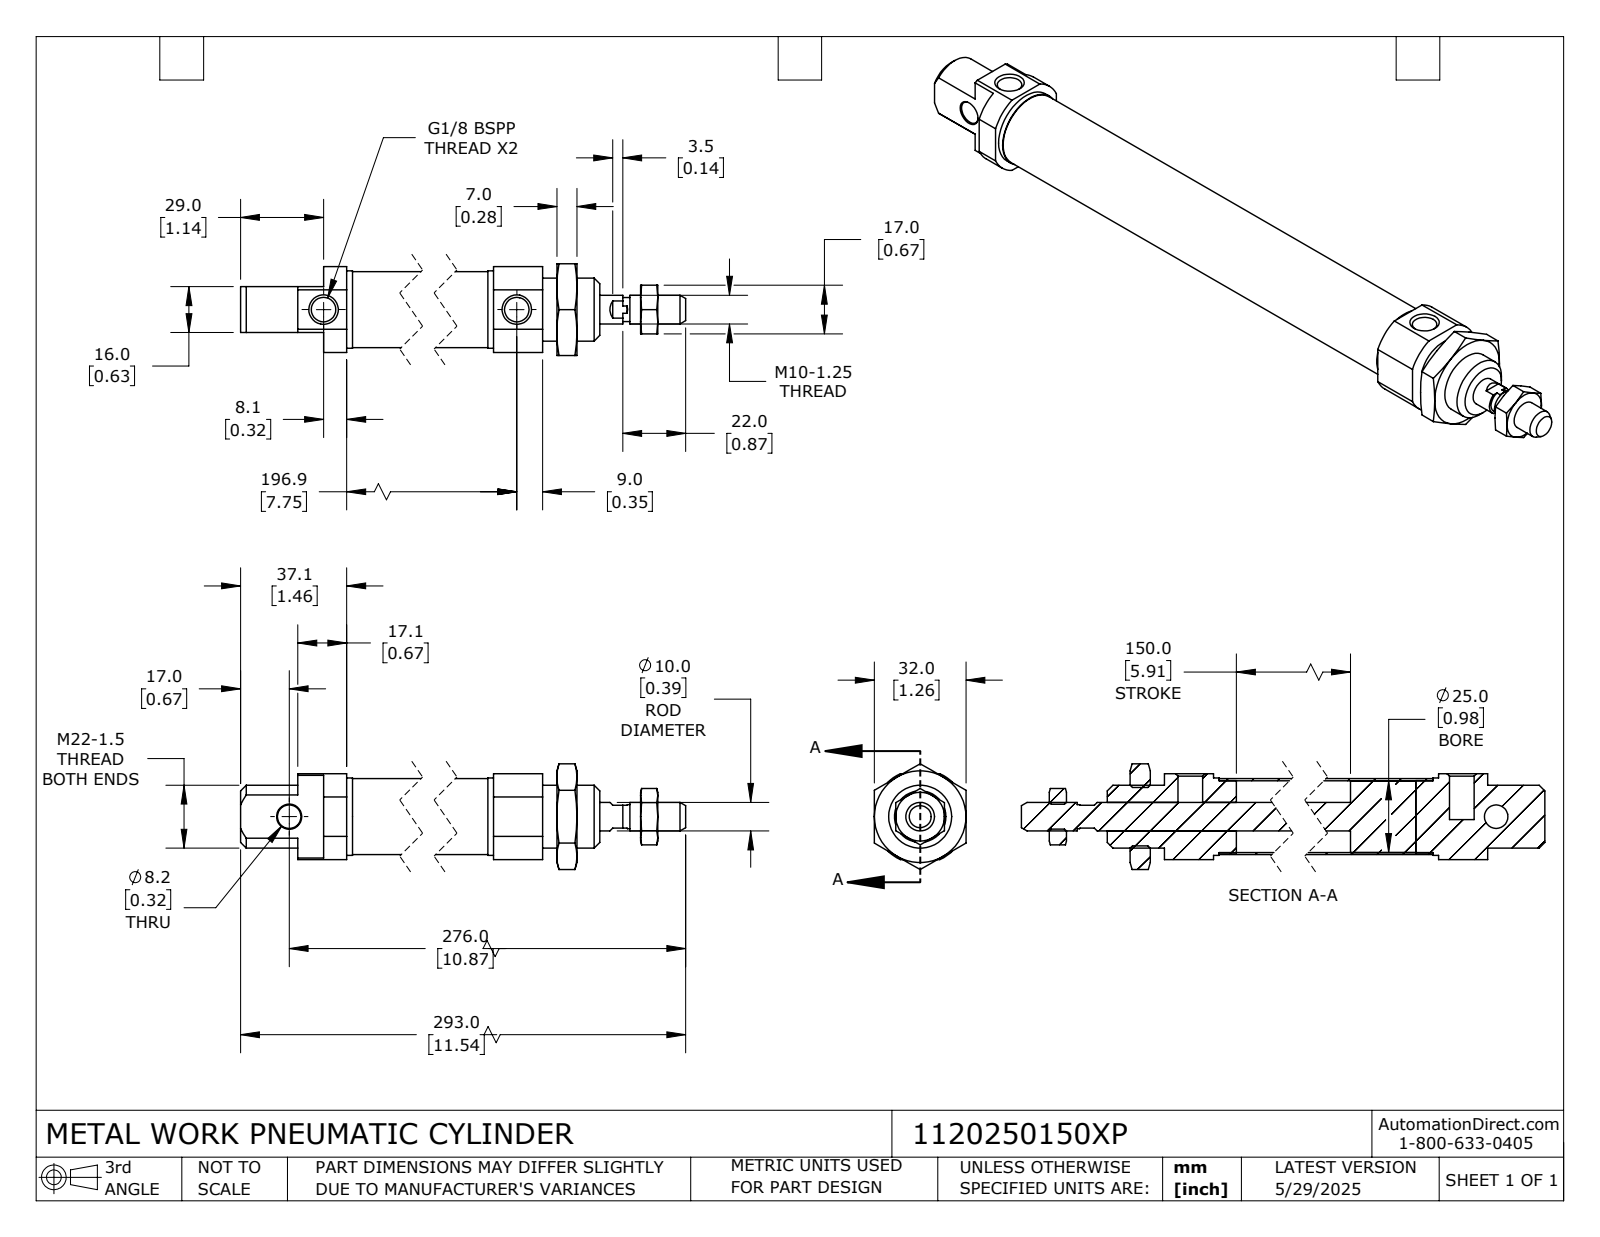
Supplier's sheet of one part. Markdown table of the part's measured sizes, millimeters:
| quantity | value |
| --- | --- |
| part name | 1120250150XP_BODY; 1120250150XP_ROD; 1120250150XP |
| STEP written by | SolidWorks 2024 (CONFIG_CONTROL_DESIGN) |
| units | millimeters |
| bodies | 6 solids, 144 faces (54 planar, 44 cylindrical, 46 other) |
| overall size | 293 × 36.95 × 32 |
| volume | 85 623 mm³ |
| surface area | 55 548 mm² |
| round holes (diameter × count) | 8.57 × 2, 8.2 × 1, 8.65 × 1, 20.38 × 1, 25 × 1 |
| round bosses / shafts (diameter × count) | 27 × 1, 26.52 × 1, 25.15 × 1, 22 × 1, 10 × 1, 8.4 × 1 |
| partial cylindrical surfaces (radius × count) | 16.5 × 1 |
| main face-to-face distances | 7, 8, 37.1, 23, 30, 217.9, 197.9, 25.1, 16, 180.8 |
| hole center spacings | 205 |
